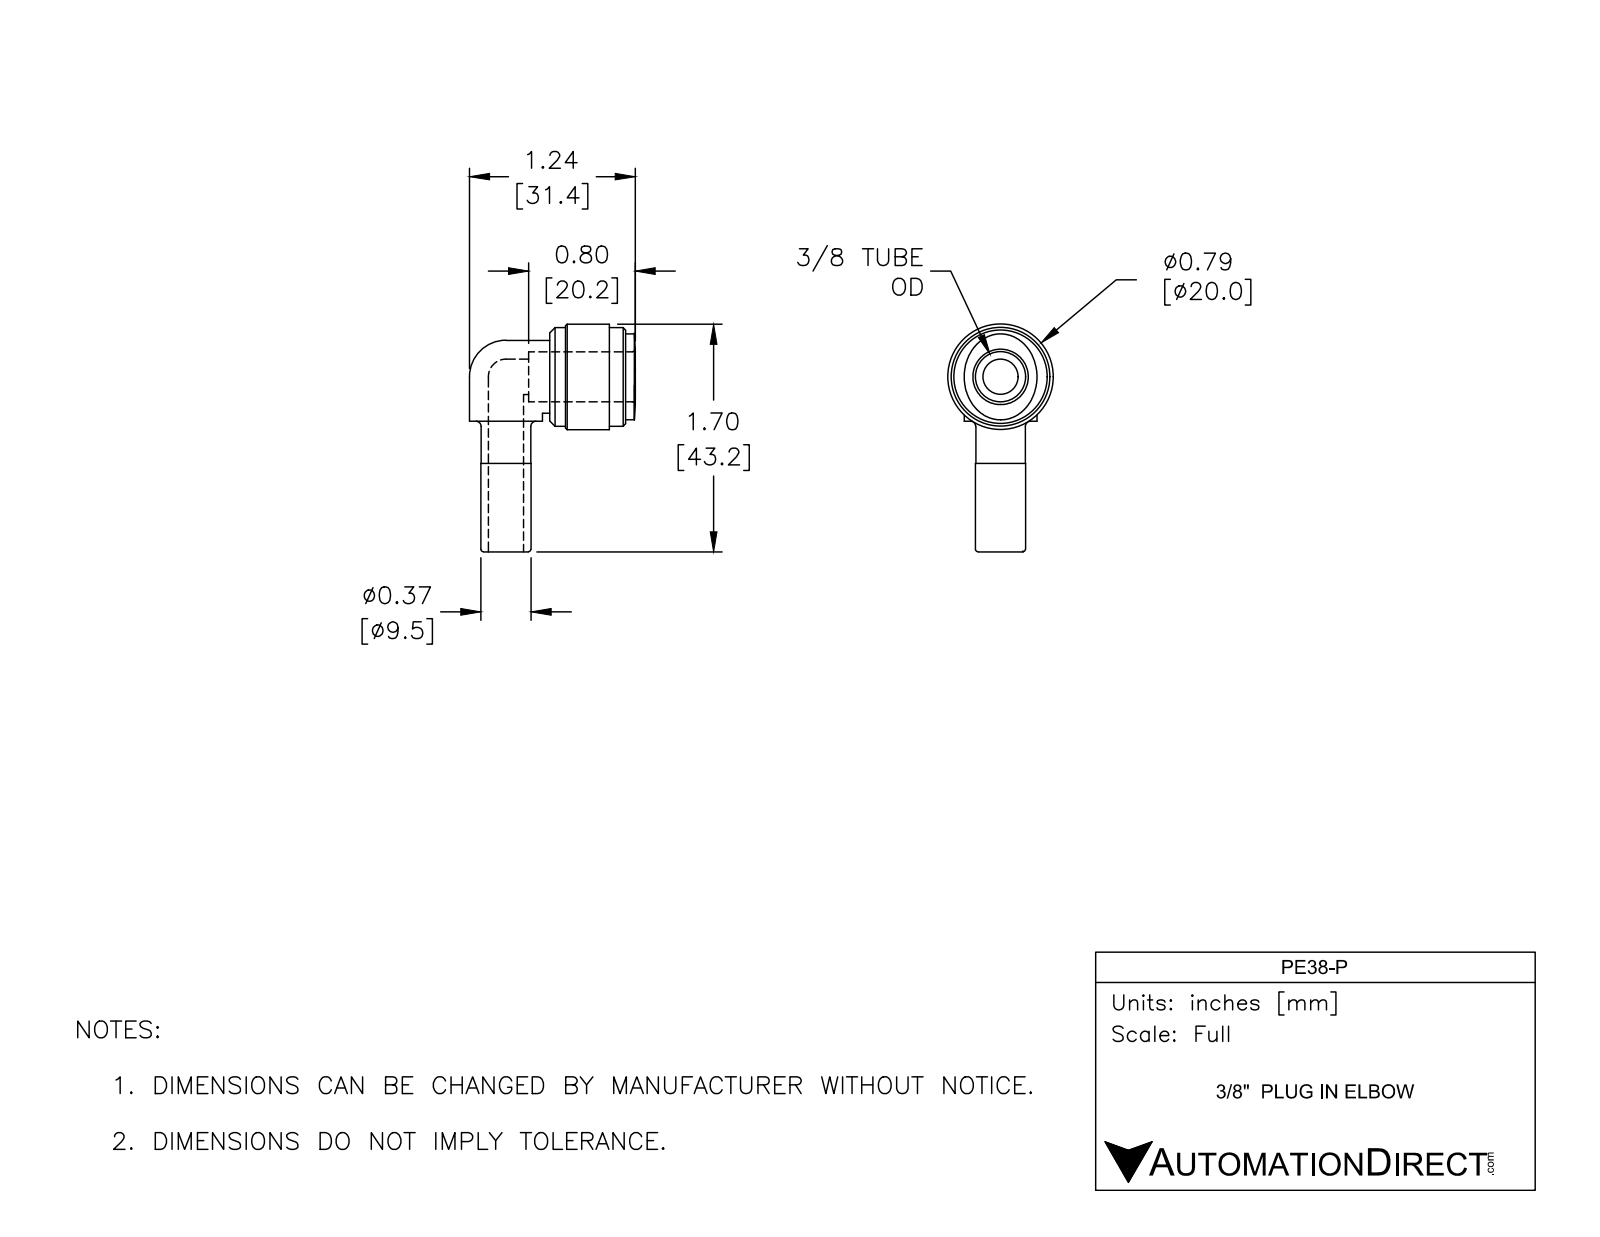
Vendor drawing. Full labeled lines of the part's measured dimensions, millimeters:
Part name (STEP PRODUCT): PE38-P
STEP written by: SolidWorks 2017 (AUTOMOTIVE_DESIGN)
Units: millimetres
Bodies: 1 solid, 48 faces (8 planar, 20 cylindrical, 20 other)
Overall size (bounding box): 43.2 × 31.4 × 20
Volume: 5 960 mm³ · Surface area: 4 232 mm²
Round holes (diameter × count): ⌀6.7 ×2, ⌀9.5 ×1
Round bosses / shafts (diameter × count): ⌀13.8 ×2, ⌀20 ×1, ⌀18.7 ×1, ⌀9.5 ×1, ⌀9.4 ×1
Main face-to-face distances: 14.4, 11.3, 3.1, 4, 15.3, 18.4, 24.8, 7, 3, 8.3
